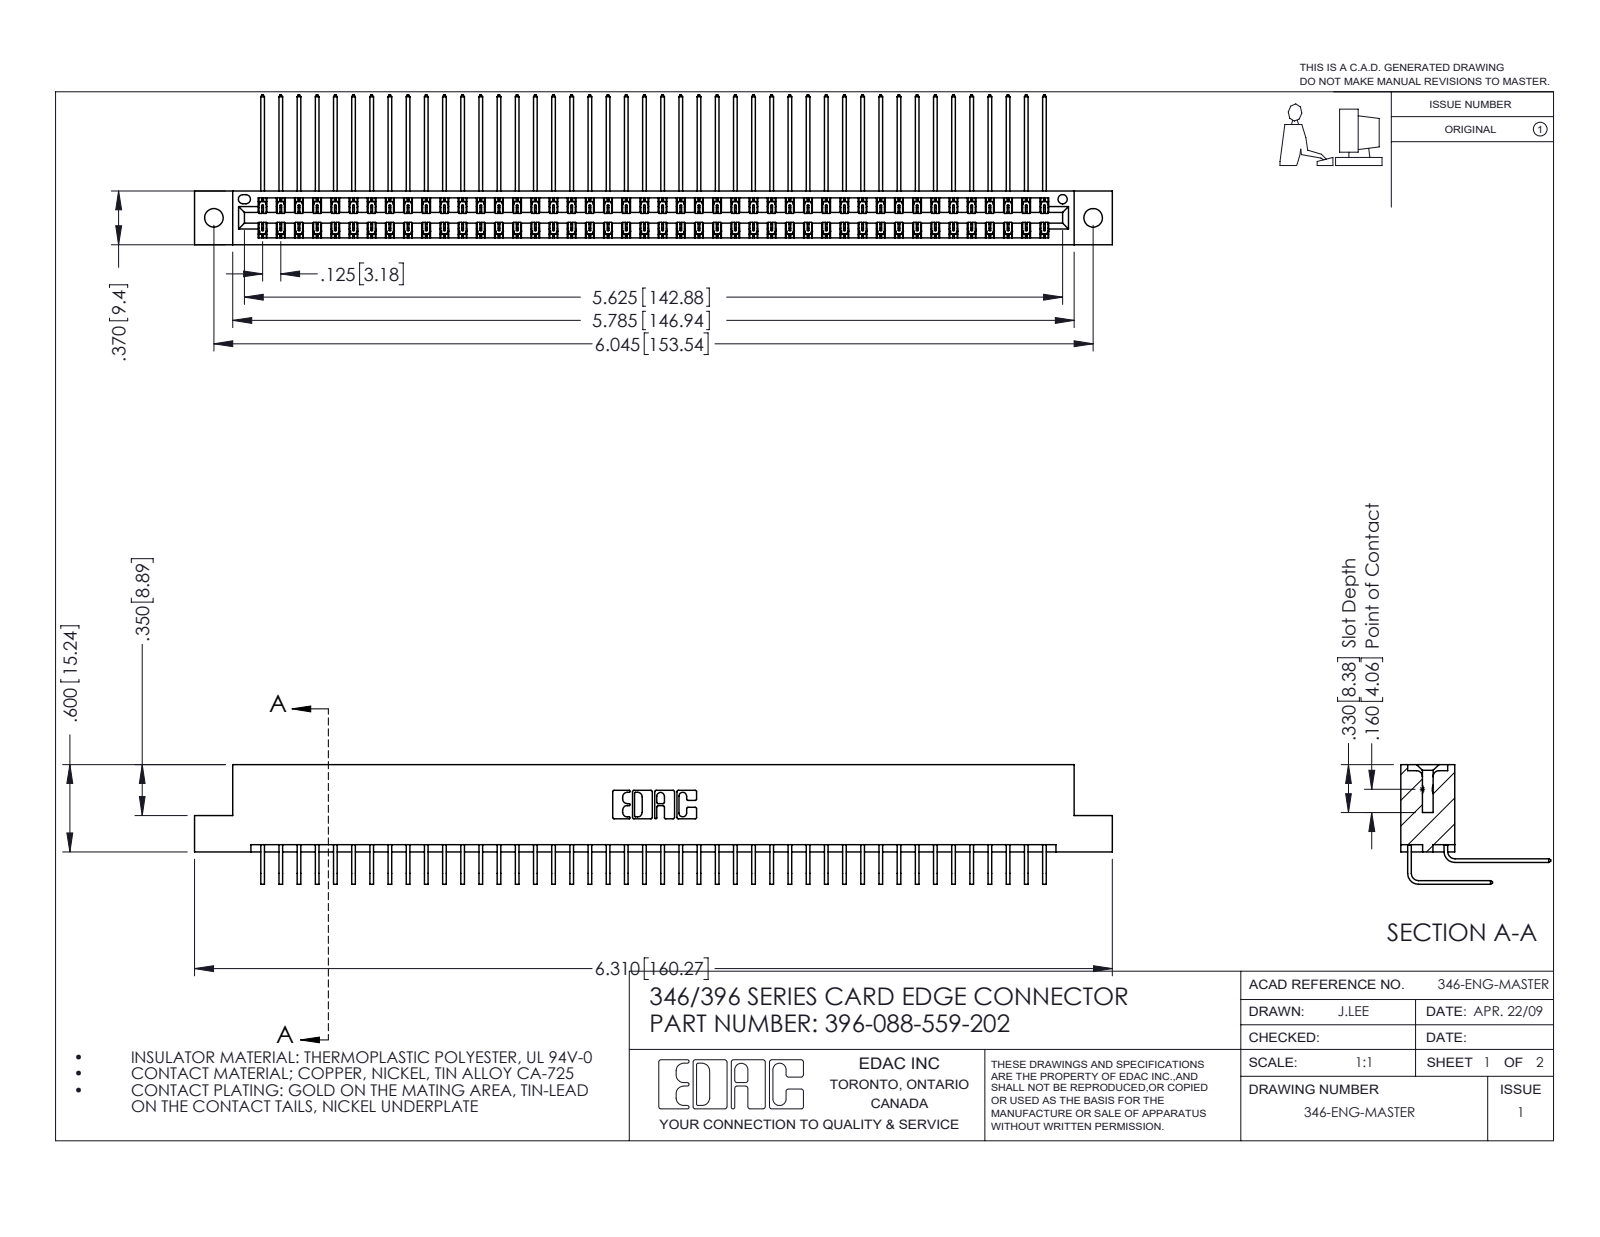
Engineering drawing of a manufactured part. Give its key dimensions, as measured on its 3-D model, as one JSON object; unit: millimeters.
{"part_name": "346 Part_Flush Mounting Lugs - 0.128 Dia; 345-292-001_559 Tail - 2; 396-088-559-202; 345-292-001_558 559 Tail - 1", "step_written_by": "SolidWorks 2016 (CONFIG_CONTROL_DESIGN)", "units": "millimeters", "bodies": {"solids": 89, "faces": 4874, "planar": 3332, "cylindrical": 1542, "other": 0}, "overall_size": [160.3, 26.2, 20.9], "volume_mm3": 16100, "surface_area_mm2": 24350, "round_holes": [[3.3, 2], [1.6, 1]], "partial_cylinders_radius": [[0.2, 132], [0.3, 22], [0.2, 6], [0.8, 6], [0.7, 3], [0.4, 2], [0.6, 2], [0.6, 2]], "face_to_face_distances": [1.2, 8.2, 0.6, 9.4, 6.4, 1.8, 7.6, 7, 3.8, 5.6], "hole_center_spacings": [6.2, 148.2, 153.5]}
